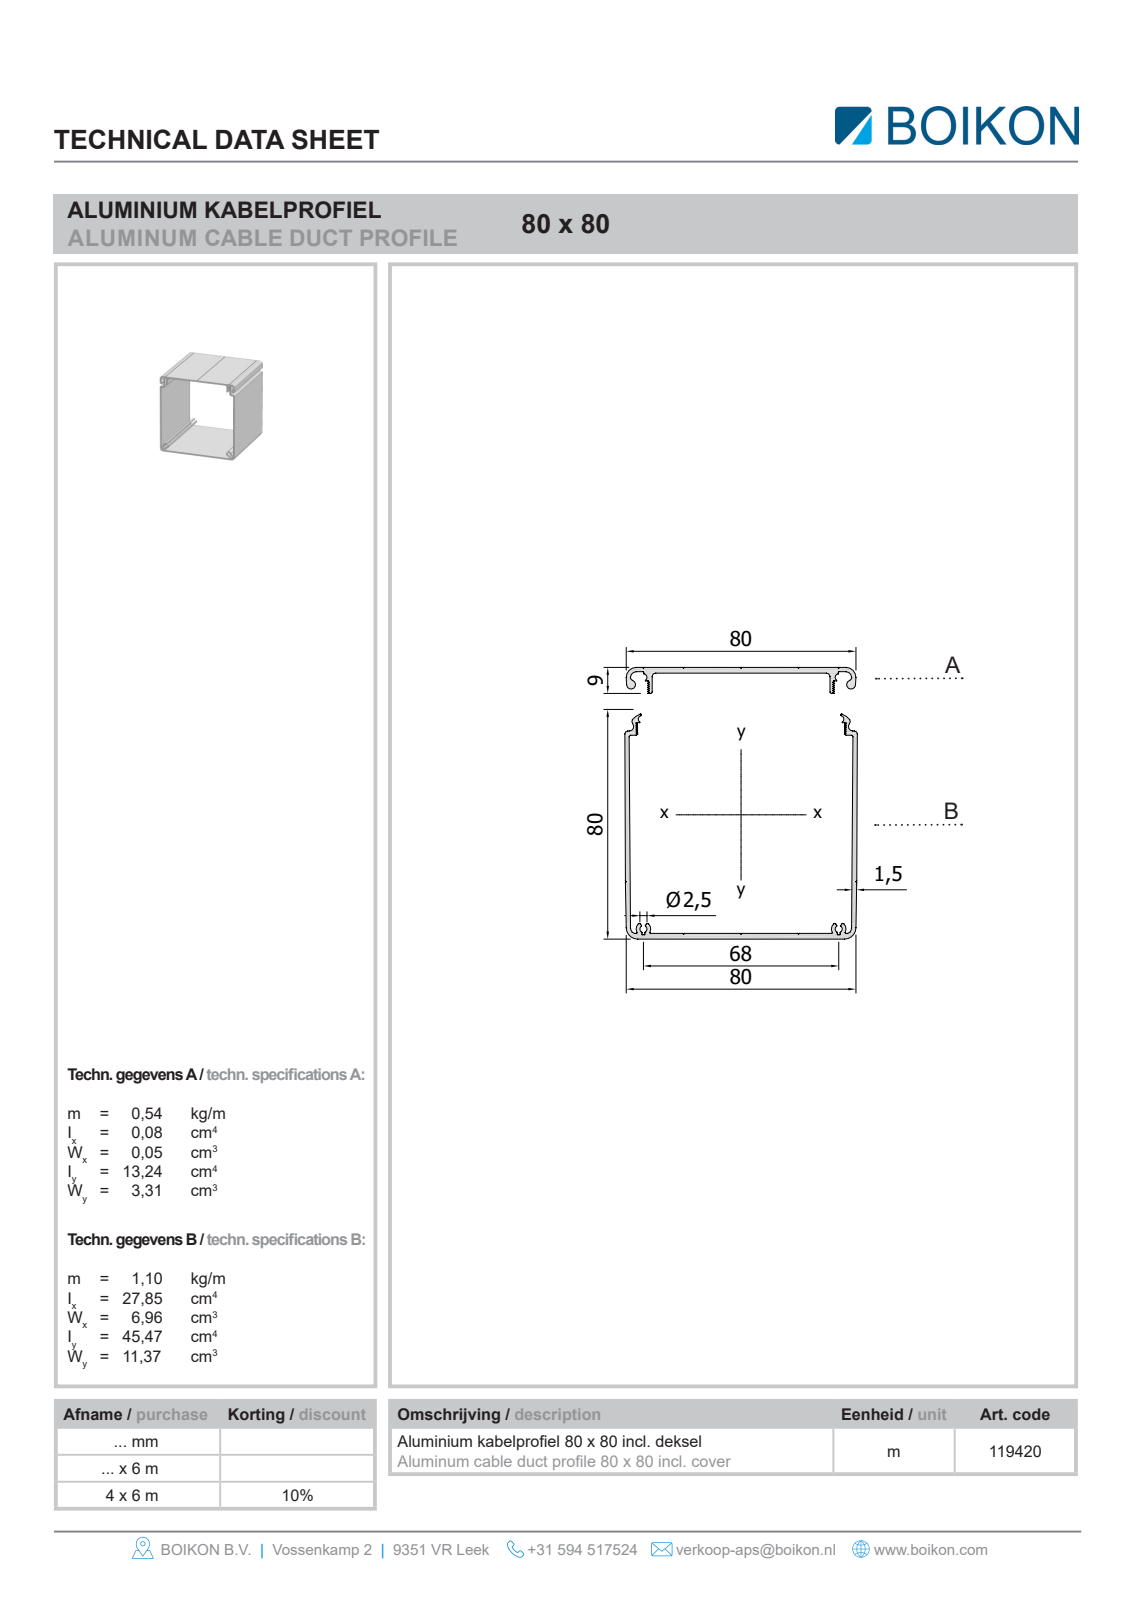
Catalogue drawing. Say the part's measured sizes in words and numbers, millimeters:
The part is named "Root; 119420Kabelgootprofiel 80x80BOIKON0". Its 3-D file was written by "HiCAD 2013 1802.4 Build 509 (AUTOMOTIVE_DESIGN)". It is 2 solids with 162 faces: 85 planar, 77 cylindrical and 0 other. Overall it measures 1000 by 80 by 80 millimeters. Its volume is 558 739 cubic millimeters and its surface area 747 320 square millimeters. Partial cylindrical surfaces (rounded edges, fillets, slot ends): 22 of radius 0.5, 12 of radius 0.3, 11 of radius 0.12, 6 of radius 1.5, 6 of radius 2, 4 of radius 3, 4 of radius 3.5, 2 of radius 0.25. The main face-to-face distances are 1.5, 78.5, 80, 77, 4, 74.5, 7.1, 71.4, 3.1, 67.4.
